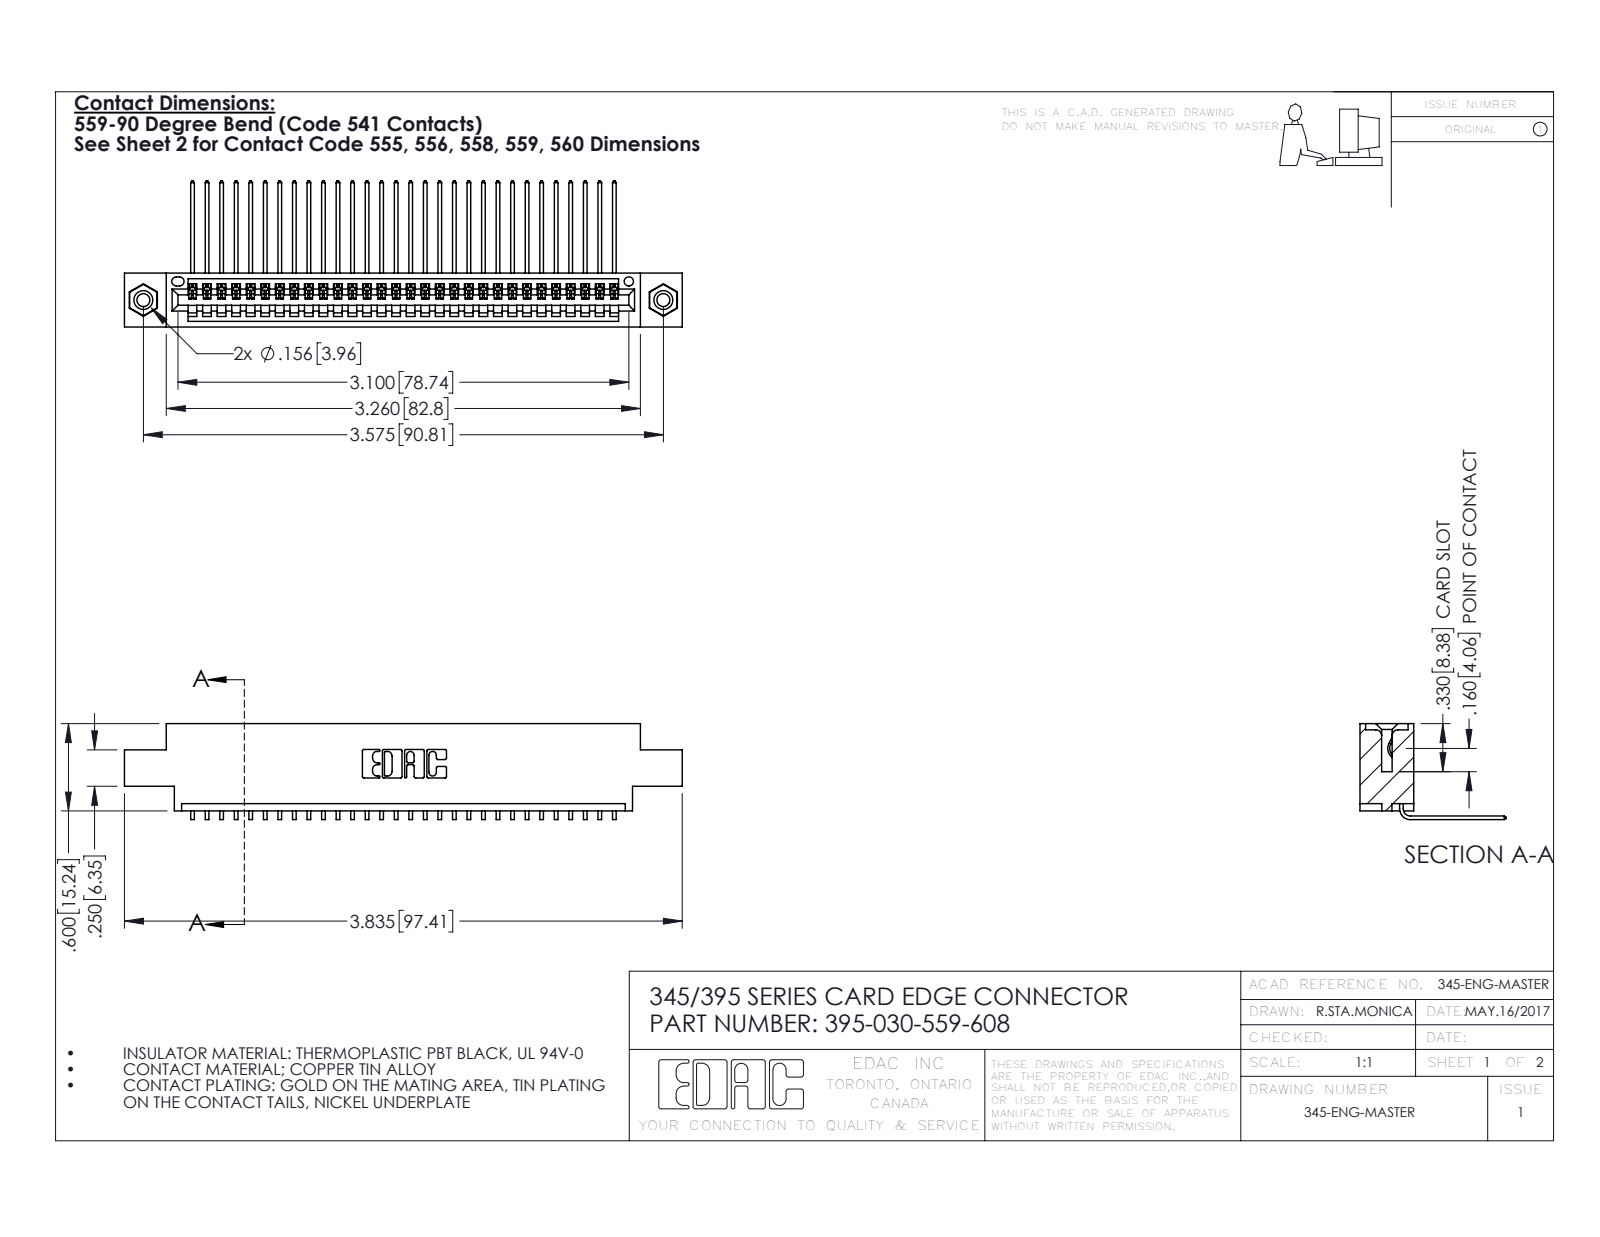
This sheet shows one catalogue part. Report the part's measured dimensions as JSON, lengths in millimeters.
{"part_name": "345 Part_0.170 Offset - 0.156 Dia-TI; 345-250-001_345-250-003-102; 395-030-559-608; 345-292-001_558 559 Tail - 1", "step_written_by": "SolidWorks 2016 (CONFIG_CONTROL_DESIGN)", "units": "millimeters", "bodies": {"solids": 33, "faces": 1990, "planar": 1376, "cylindrical": 598, "other": 16}, "overall_size": [97.4, 25.5, 16.7], "volume_mm3": 9130, "surface_area_mm2": 12710, "round_holes": [[2.3, 2], [3.2, 2], [4, 2], [1.6, 1]], "round_bosses_or_shafts": [[3.9, 2]], "partial_cylinders_radius": [[0.2, 60], [0.3, 22], [0.2, 6], [0.8, 6], [0.7, 3], [0.8, 2], [1, 2], [0.4, 1]], "face_to_face_distances": [1.8, 7.6, 9.4, 5.1, 2.5, 6.9, 0.6, 5.7, 4.4, 3.8], "hole_center_spacings": [6.9, 84.8, 90.8]}
